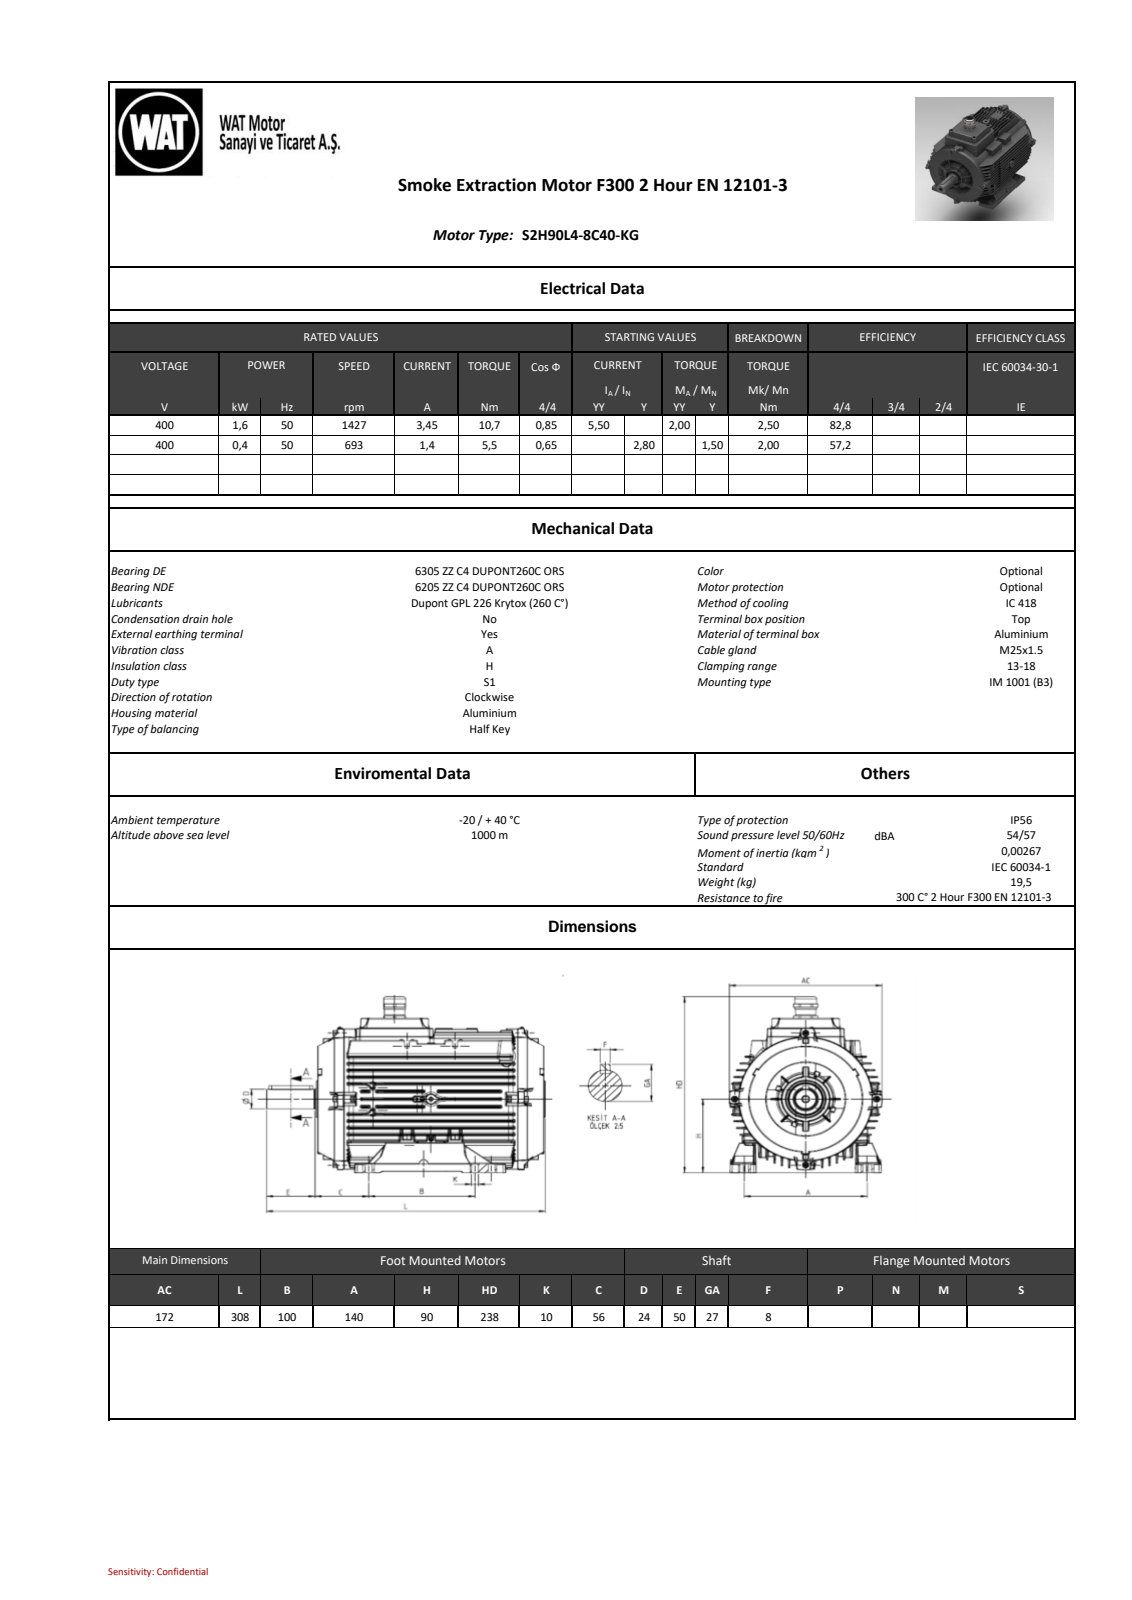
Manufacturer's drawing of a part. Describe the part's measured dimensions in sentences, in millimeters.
The part is named "2603BE5CCA1Cd4gv". Its 3-D file was written by "SIEMENS PLM Software NX 11.0 (AUTOMOTIVE_DESIGN)". It is 0 solids with 7404 faces: 1600 planar, 2461 cylindrical and 3343 other. Overall it measures 346.04 by 238 by 172.19 millimeters. Round holes: 6 of diameter 3.5, 1 of diameter 4.72, 1 of diameter 6.8, 1 of diameter 8.4, 1 of diameter 18, 1 of diameter 32, 1 of diameter 36.9, 1 of diameter 40. Round bosses or shafts: 8 of diameter 9.2, 8 of diameter 8.5, 4 of diameter 8, 4 of diameter 5, 1 of diameter 29.59, 1 of diameter 28.14, 1 of diameter 26.62, 1 of diameter 25. Partial cylindrical surfaces (rounded edges, fillets, slot ends): 620 of radius 0.8, 565 of radius 1, 274 of radius 0.5, 61 of radius 0.98, 56 of radius 2, 52 of radius 0.2, 28 of radius 8, 18 of radius 1.5. The main face-to-face distances are 91.91, 7.5, 7.37, 23.57, 7.94, 82.85, 9.06, 16.43, 50.35, 74.81. The hole center spacings are 29, 50.23, 13.27, 50.22.
